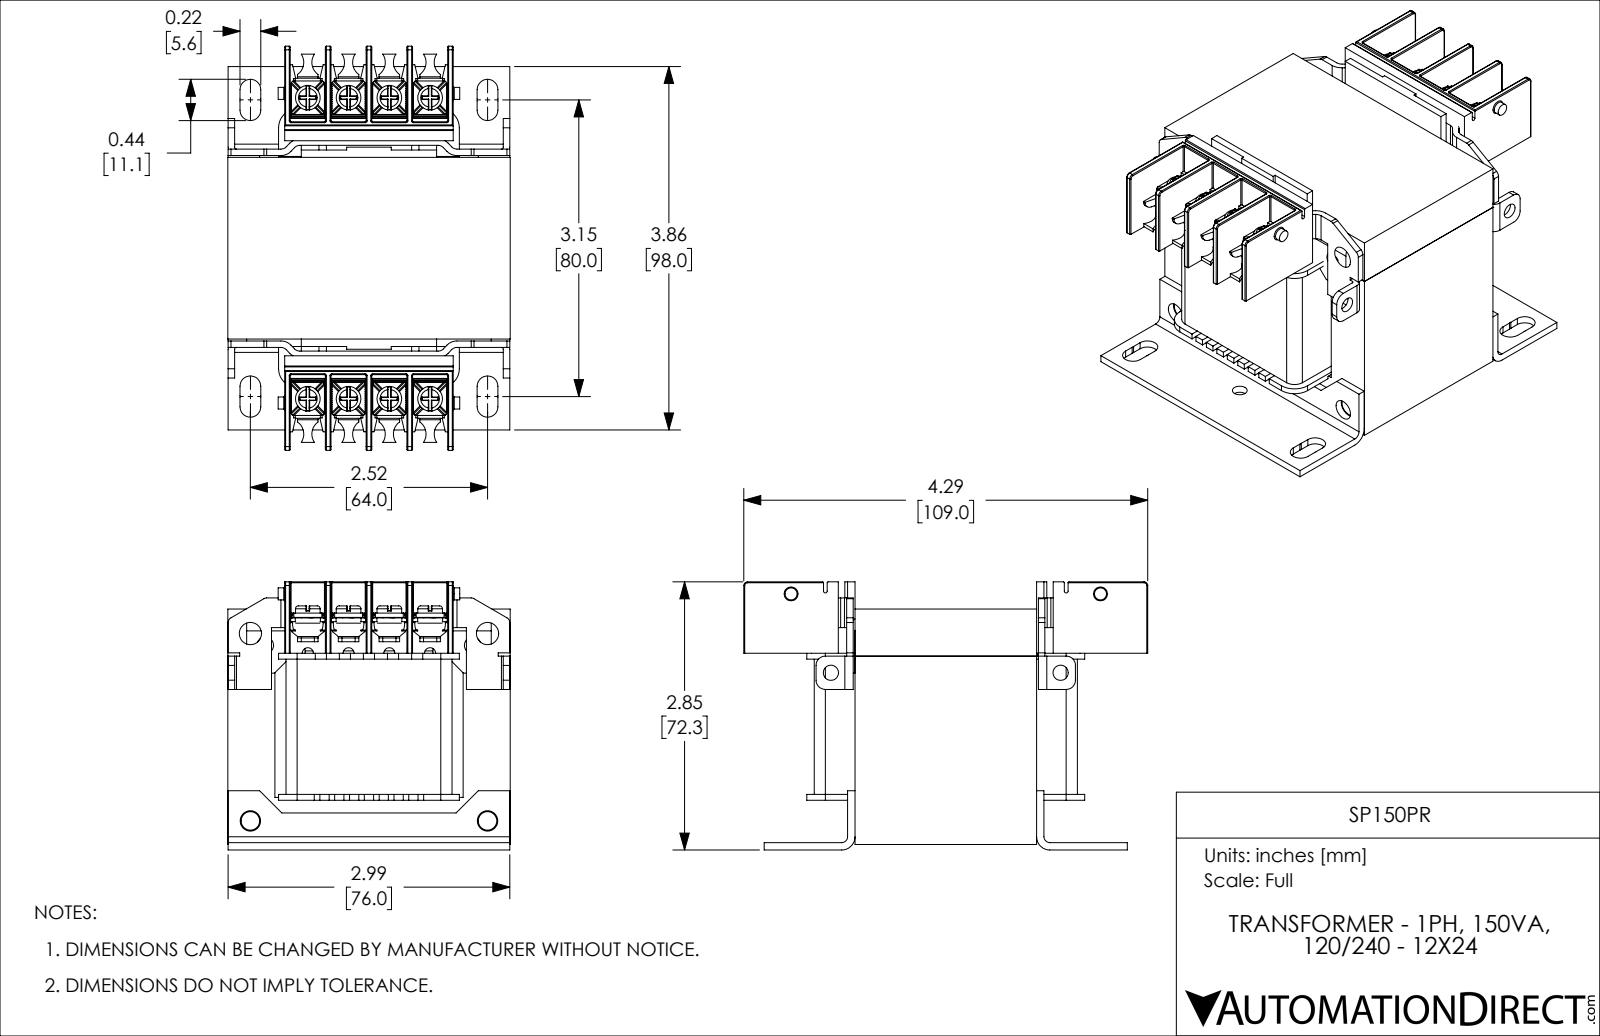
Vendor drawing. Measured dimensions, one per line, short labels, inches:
name: SP150PR
written by: SolidWorks 2018 (AUTOMOTIVE_DESIGN)
unit: in
bodies: 42 solids, 3183 faces (1948 planar, 941 cylindrical, 294 other)
size: 4.291 × 3 × 2.847
volume: 18.42 in³; area: 166 in²
holes: 10× ⌀0.157, 8× ⌀0.105, 8× ⌀0.138, 2× ⌀0.1, 2× ⌀0.161, 2× ⌀0.177, 2× ⌀0.197, 2× ⌀0.217, 2× ⌀0.236
bosses: 8× ⌀0.262, 8× ⌀0.24, 8× ⌀0.168, 8× ⌀0.11, 3× ⌀0.128
rounds: 52× R0.005, 52× R0.01, 46× R0.012, 32× R0.029, 18× R0.059, 16× R0.157, 12× R0.035, 10× R0.079
face distances: 0.5, 2, 0.059, 0.433, 0.079, 2.5, 2.382, 1, 1.929, 1.5
hole spacings: 0.433, 0.866, 3.216, 1.299, 3.187, 3.303, 3.207, 3.226
